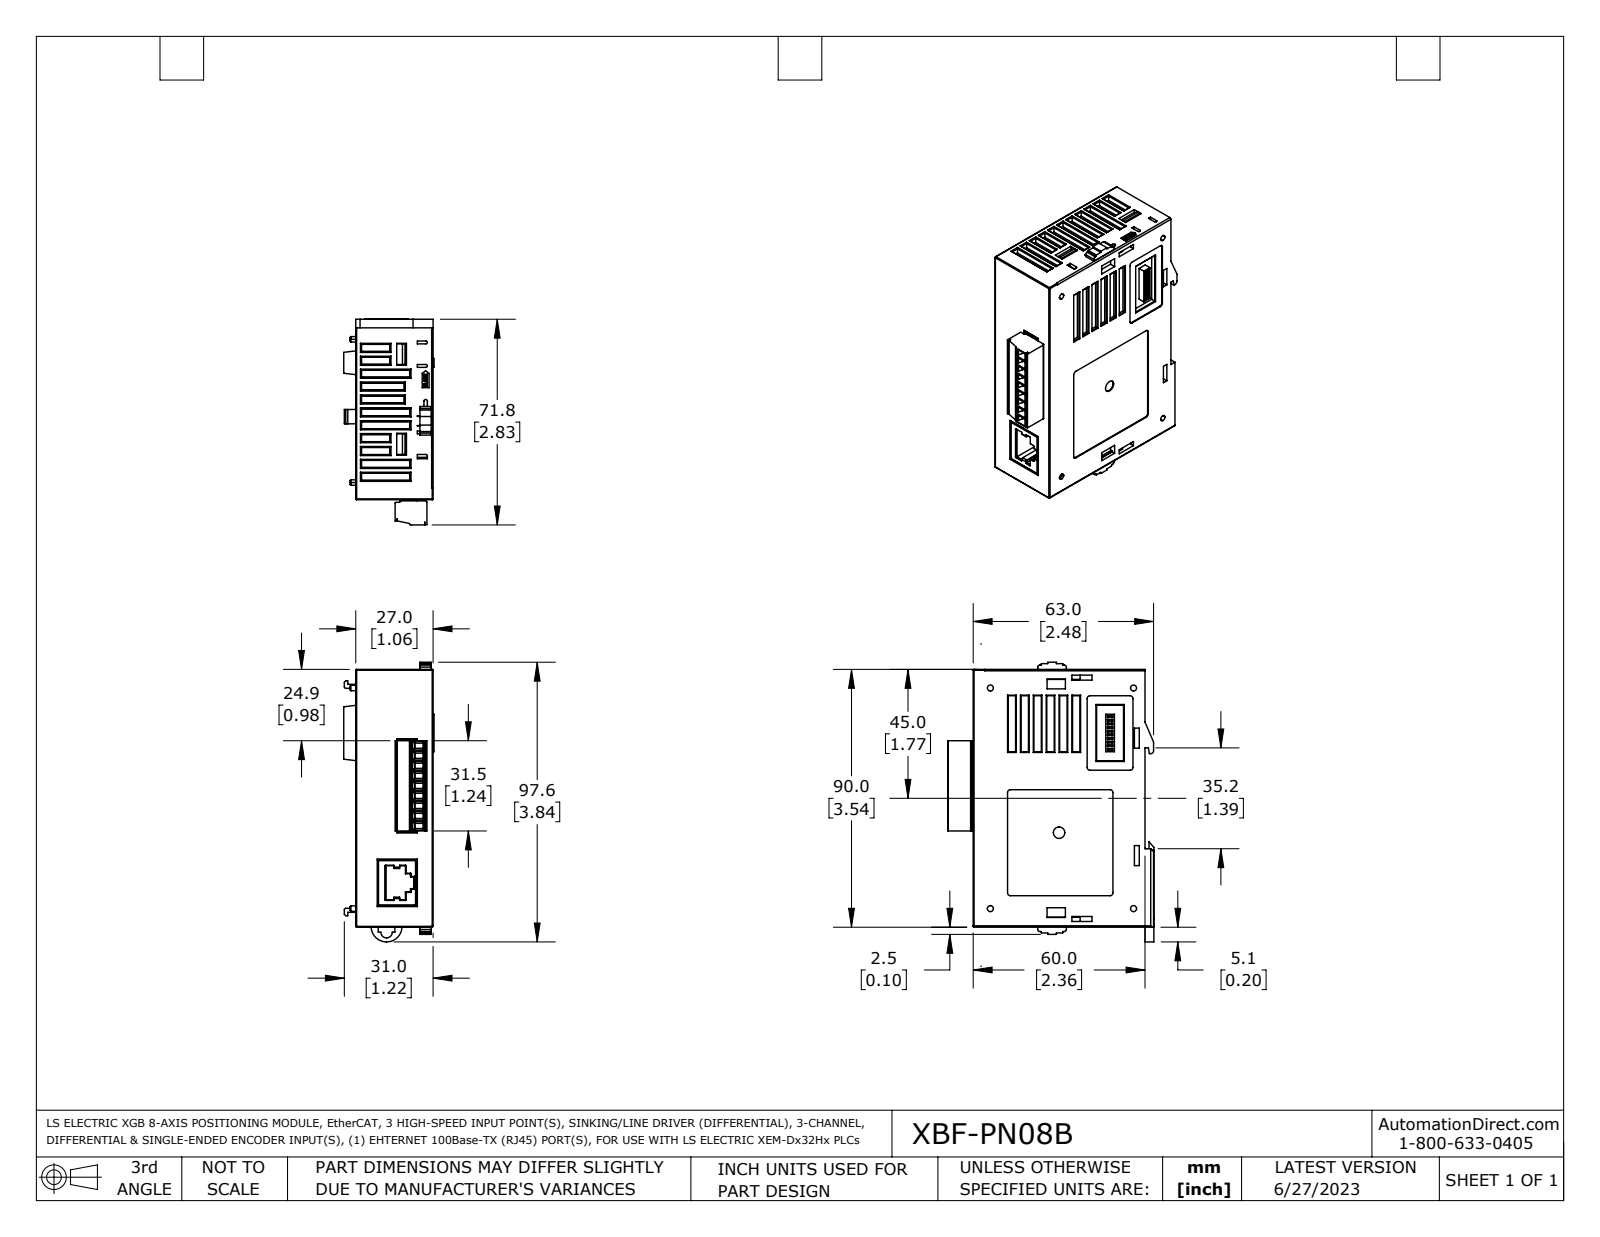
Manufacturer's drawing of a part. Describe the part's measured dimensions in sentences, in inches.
The part is named "XBF-PN08B broken 5 faces 1 ext1 coord". Its 3-D file was written by "SolidWorks 2021 (AUTOMOTIVE_DESIGN)". It is 1 solid with 2701 faces: 2001 planar, 489 cylindrical and 211 other. Overall it measures 3.844 by 2.831 by 1.241 inches. Its volume is 8.68 cubic inches and its surface area 51.52 square inches. Round holes: 9 of diameter 0.047, 9 of diameter 0.108, 9 of diameter 0.116, 4 of diameter 0.083, 2 of diameter 0.071, 1 of diameter 0.157. Round bosses or shafts: 9 of diameter 0.11, 4 of diameter 0.075, 2 of diameter 0.071. Partial cylindrical surfaces (rounded edges, fillets, slot ends): 56 of radius 0.004, 48 of radius 0.008, 34 of radius 0.012, 23 of radius 0.02, 11 of radius 0.039, 9 of radius 0.062, 9 of radius 0.071, 8 of radius 0.048. The main face-to-face distances are 1.063, 0.079, 0.039, 0.984, 2.362, 1.051, 0.945, 1.024, 0.067, 0.031. The hole center spacings are 0.138, 0.276, 0.413, 0.551, 0.689, 0.827, 0.965, 0.539.
